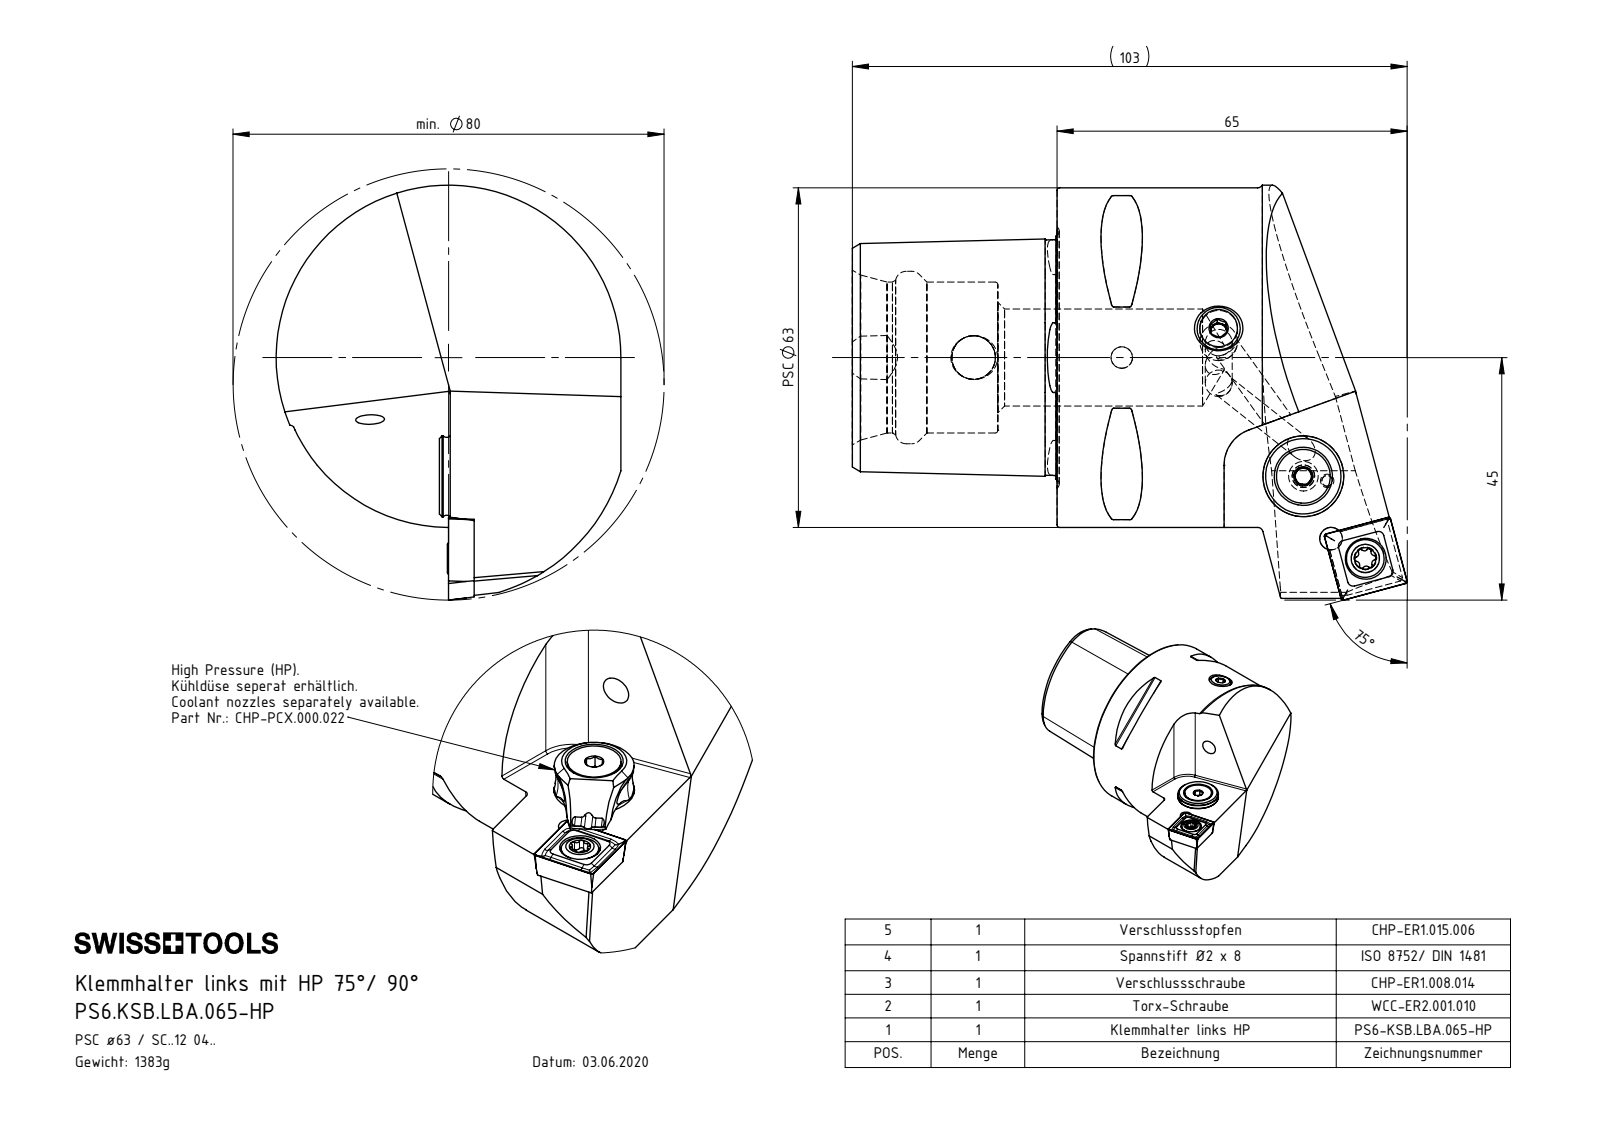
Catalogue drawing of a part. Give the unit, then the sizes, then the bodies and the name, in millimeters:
Units: millimetres
Overall size (bounding box): 103 × 77 × 64
Round holes (diameter × count): ⌀4.2 ×4, ⌀5 ×2, ⌀1.2 ×1, ⌀2 ×1, ⌀2.5 ×1, ⌀3 ×1, ⌀4 ×1, ⌀5.2 ×1, ⌀5.5 ×1, ⌀7 ×1, ⌀7.6 ×1, ⌀8.1 ×1
Round bosses / shafts (diameter × count): ⌀5 ×2, ⌀63 ×1, ⌀15 ×1, ⌀13.4 ×1, ⌀10 ×1, ⌀8 ×1, ⌀7 ×1, ⌀5.5 ×1
Partial cylindrical surfaces — rounded edges, fillets, slot ends (radius × count): R0.5 ×10, R0.39 ×6, R0.69 ×3, R0.69 ×3, R6 ×1, R7 ×1, R32 ×1, R34 ×1
Main face-to-face distances: 38, 24.88, 31.7, 27.2, 4.5, 27, 11, 27.24, 4.46, 69
Hole centre spacings: 4.49, 7.36, 7.45, 10.72, 12.65, 16.04, 16.12, 19.1
Volume: 176 061 mm³ · Surface area: 31 969 mm²
Bodies: 8 solids, 373 faces (89 planar, 99 cylindrical, 185 other)
Part name (STEP PRODUCT): CHP-ER1.015.006_A; CHP-ER1.015.006; SCMT120404; CHP-ER1.008.014_A (+6 more)
STEP written by: SolidWorks 2017 (AUTOMOTIVE_DESIGN)
